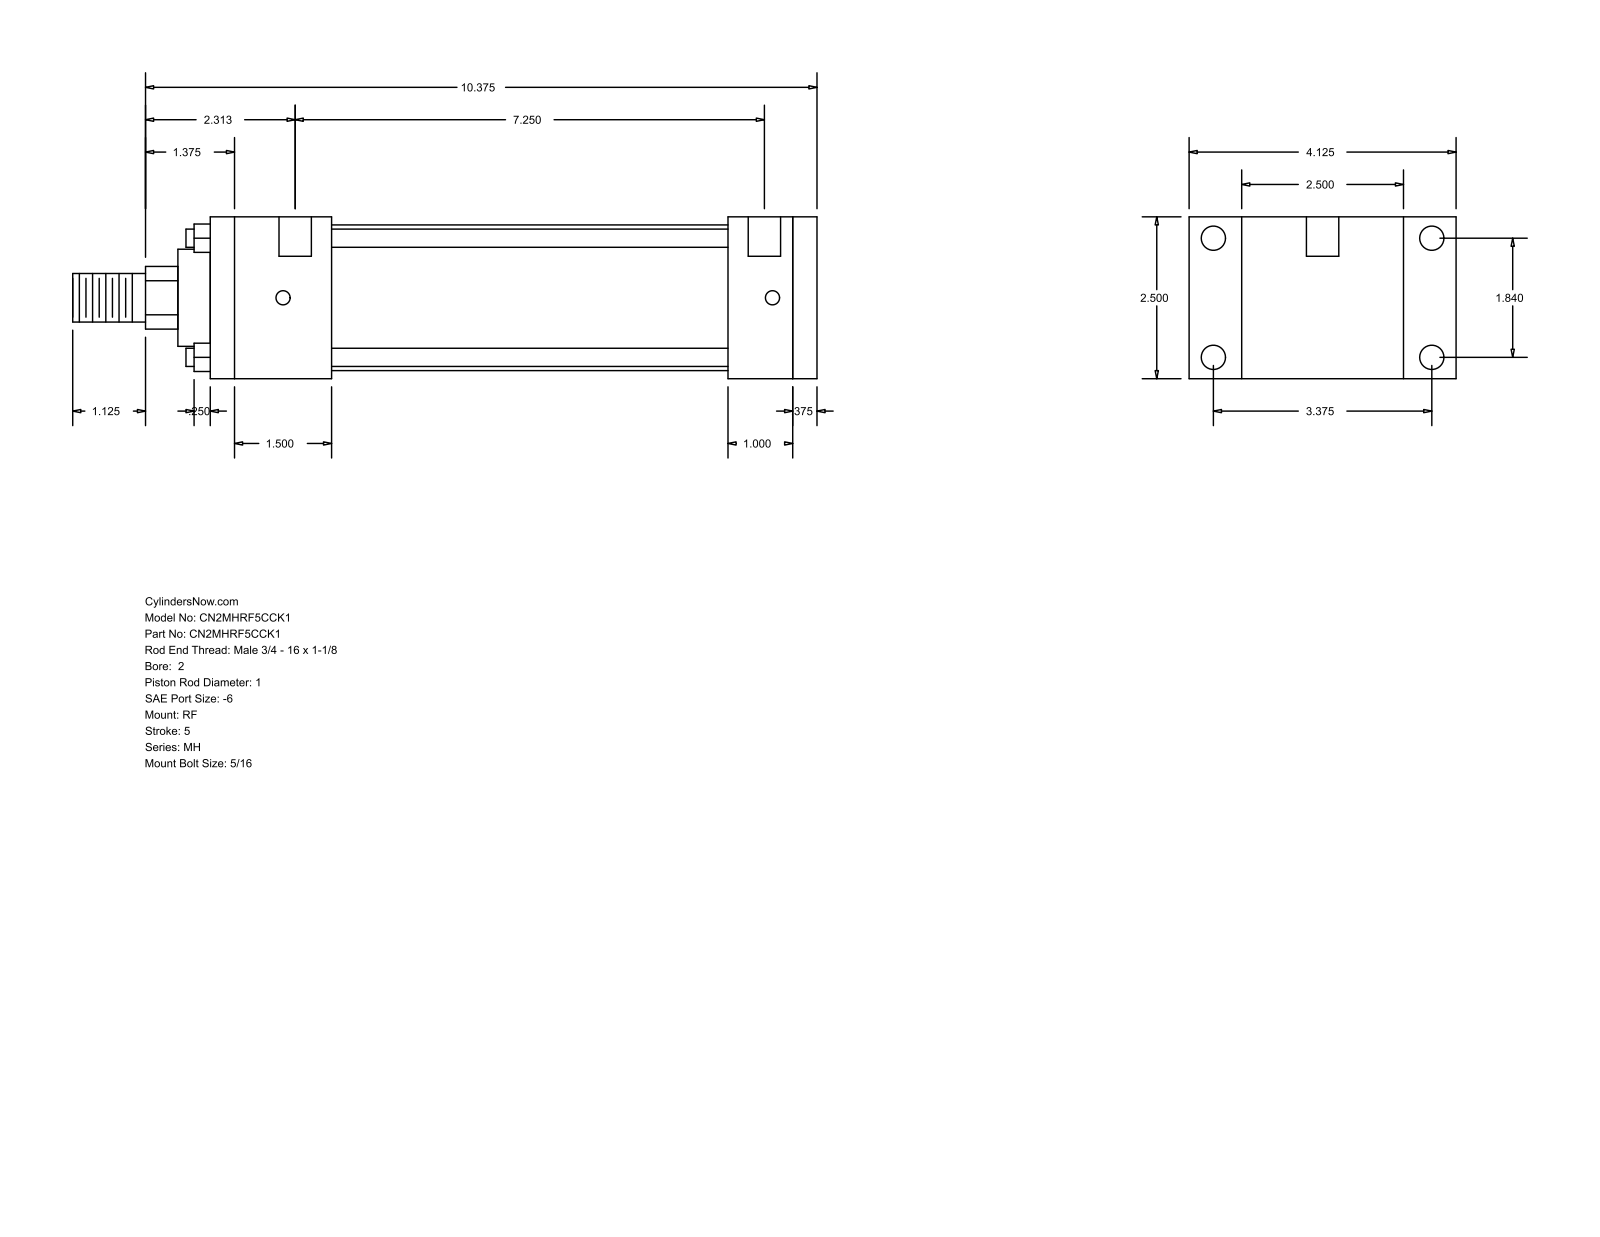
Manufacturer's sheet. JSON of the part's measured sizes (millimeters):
{"part_name": "MH_RF__0200_1", "step_written_by": "GSSL Pune (CONFIG_CONTROL_DESIGN)", "units": "millimeters", "bodies": {"solids": 0, "faces": 92, "planar": 64, "cylindrical": 28, "other": 0}, "overall_size": [292.1, 104.78, 63.5], "round_holes": [[5.56, 4], [9.53, 4], [12.7, 2]], "round_bosses_or_shafts": [[7.14, 4], [57.15, 1], [38.1, 1], [25.4, 1], [19.05, 1]], "partial_cylinders_radius": [[12.29, 1]], "face_to_face_distances": [63.5, 238.12, 9.52, 228.6, 20.64, 25.4, 47.63, 203.2, 155.57, 180.97], "hole_center_spacings": [46.74, 85.72, 97.63, 192.08, 3.17, 4.76, 184.15, 187.32]}
